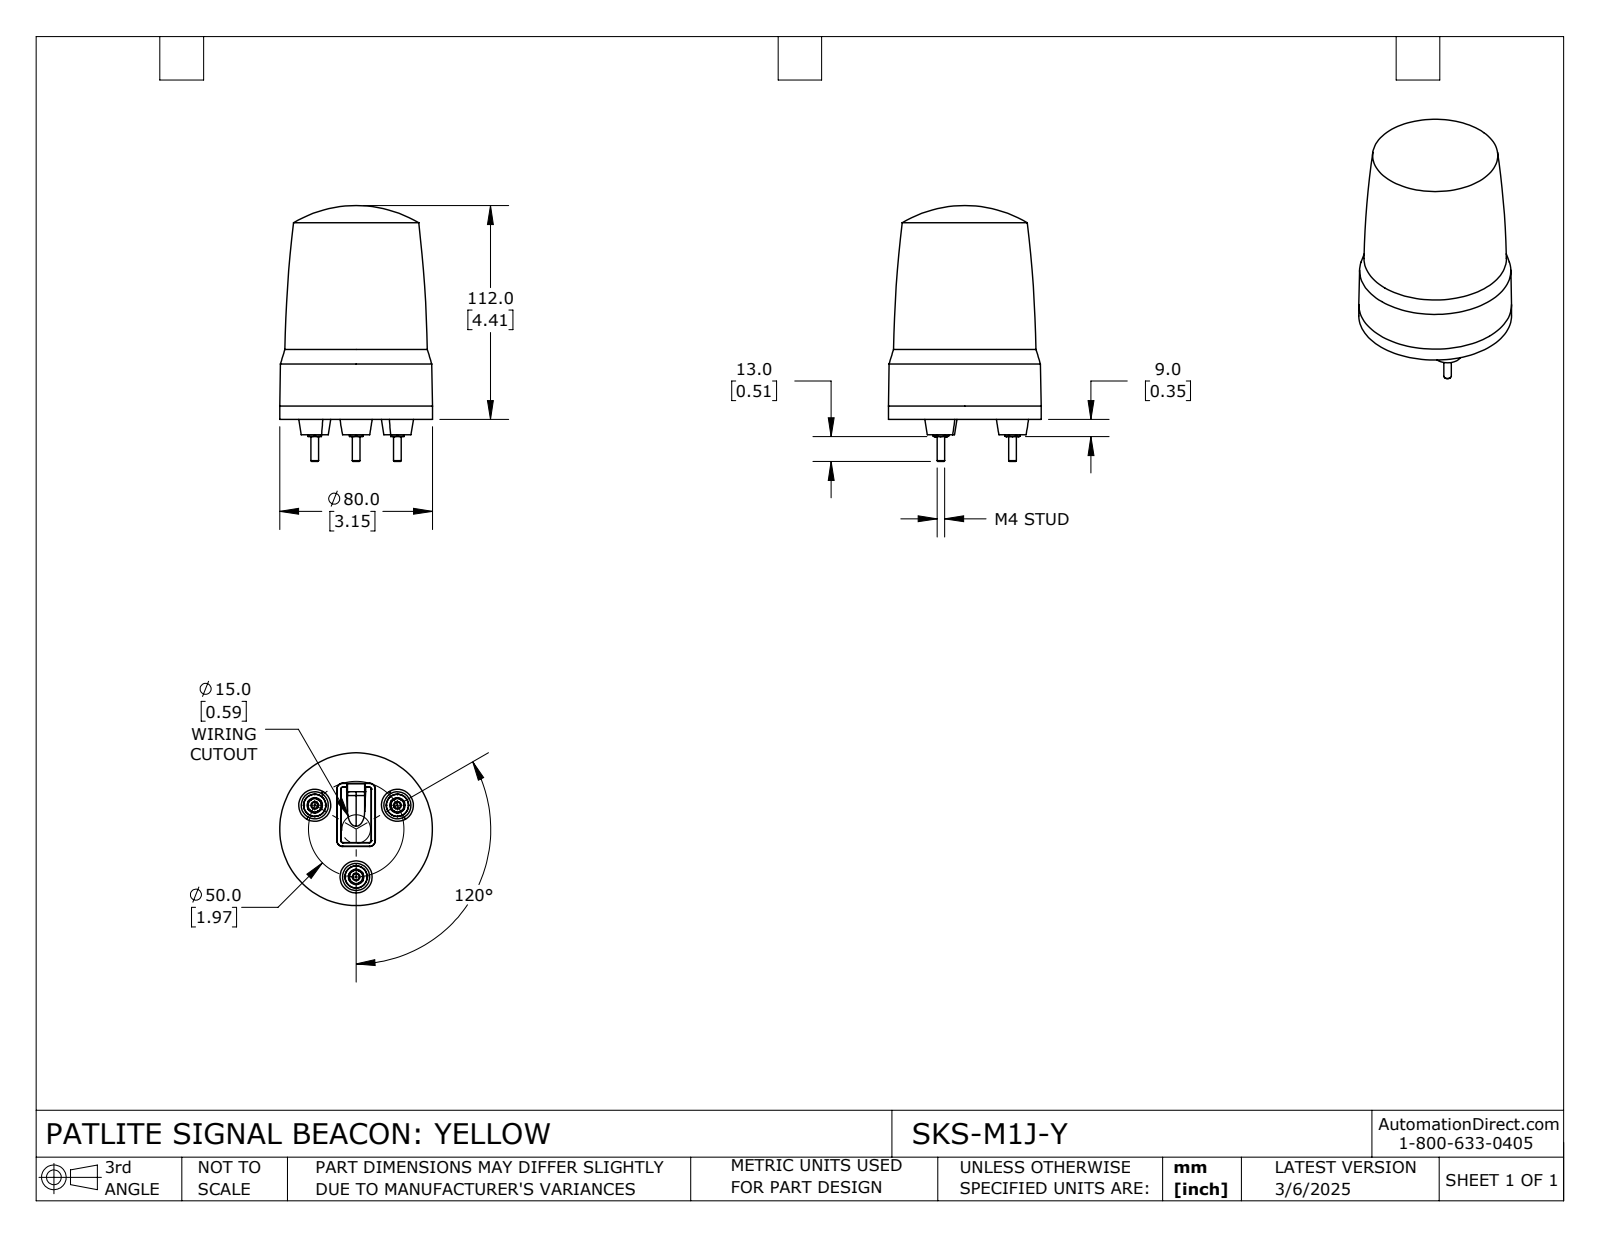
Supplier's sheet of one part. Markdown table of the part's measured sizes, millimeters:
| quantity | value |
| --- | --- |
| part name | SKS-M1J-Y |
| STEP written by | SolidWorks 2024 (CONFIG_CONTROL_DESIGN) |
| units | millimeters |
| bodies | 1 solid, 138 faces (47 planar, 14 cylindrical, 77 other) |
| overall size | 134 × 80 × 80 |
| volume | 463 225 mm³ |
| surface area | 35 408 mm² |
| round bosses / shafts (diameter × count) | 8 × 3, 4 × 3, 80 × 1 |
| main face-to-face distances | 0.85, 2.45, 1.6, 5.3, 6.15, 7.75, 2.7, 8, 8.85, 10.45 |
